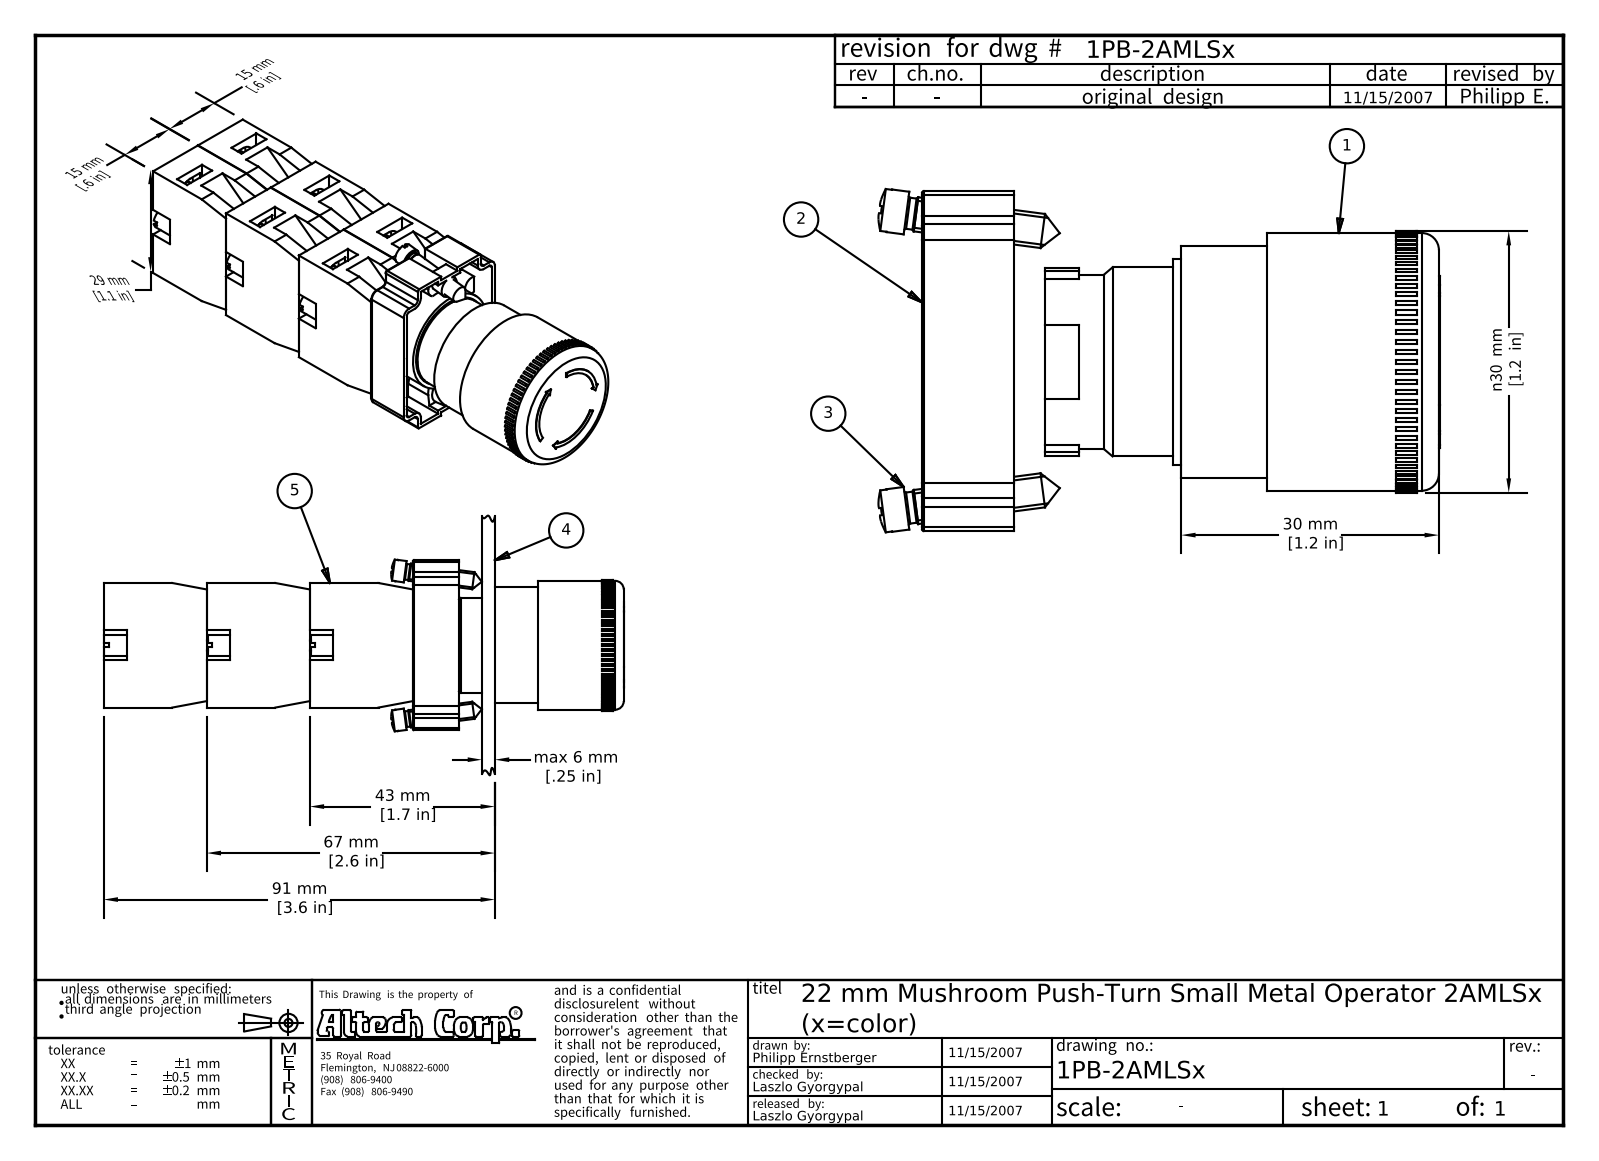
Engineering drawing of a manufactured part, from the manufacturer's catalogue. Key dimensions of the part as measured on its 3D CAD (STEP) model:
Part name (STEP PRODUCT): 2AMLSx_assembly; 2AMLSx; rubber_gasket; 2BRK (+6 more)
STEP written by: Autodesk Inventor 2008 (AUTOMOTIVE_DESIGN)
Units: millimetres
Bodies: 30 solids, 1472 faces (842 planar, 276 cylindrical, 354 other)
Overall size (bounding box): 121.2 × 60.45 × 45
Volume: 86 585 mm³ · Surface area: 47 327 mm²
Round holes (diameter × count): ⌀2.5 ×5, ⌀2.6 ×2, ⌀18 ×1, ⌀22 ×1, ⌀22.25 ×1, ⌀22.5 ×1, ⌀25 ×1, ⌀27.4 ×1
Round bosses / shafts (diameter × count): ⌀3 ×6, ⌀5 ×4, ⌀2.75 ×4, ⌀1.5 ×4, ⌀4 ×2, ⌀3.65 ×2, ⌀30 ×1, ⌀27 ×1
Partial cylindrical surfaces — rounded edges, fillets, slot ends (radius × count): R0.25 ×94, R1 ×13, R0.72 ×8, R2.25 ×5, R0.5 ×4, R0.8 ×4, R1.8 ×4, R2 ×4
Main face-to-face distances: 14.8, 14.7, 24, 3, 48, 29.5, 29, 1, 19.1, 40.1
Hole centre spacings: 14.53, 6.52, 6.57, 13, 25.88, 26, 26.27, 29.07
